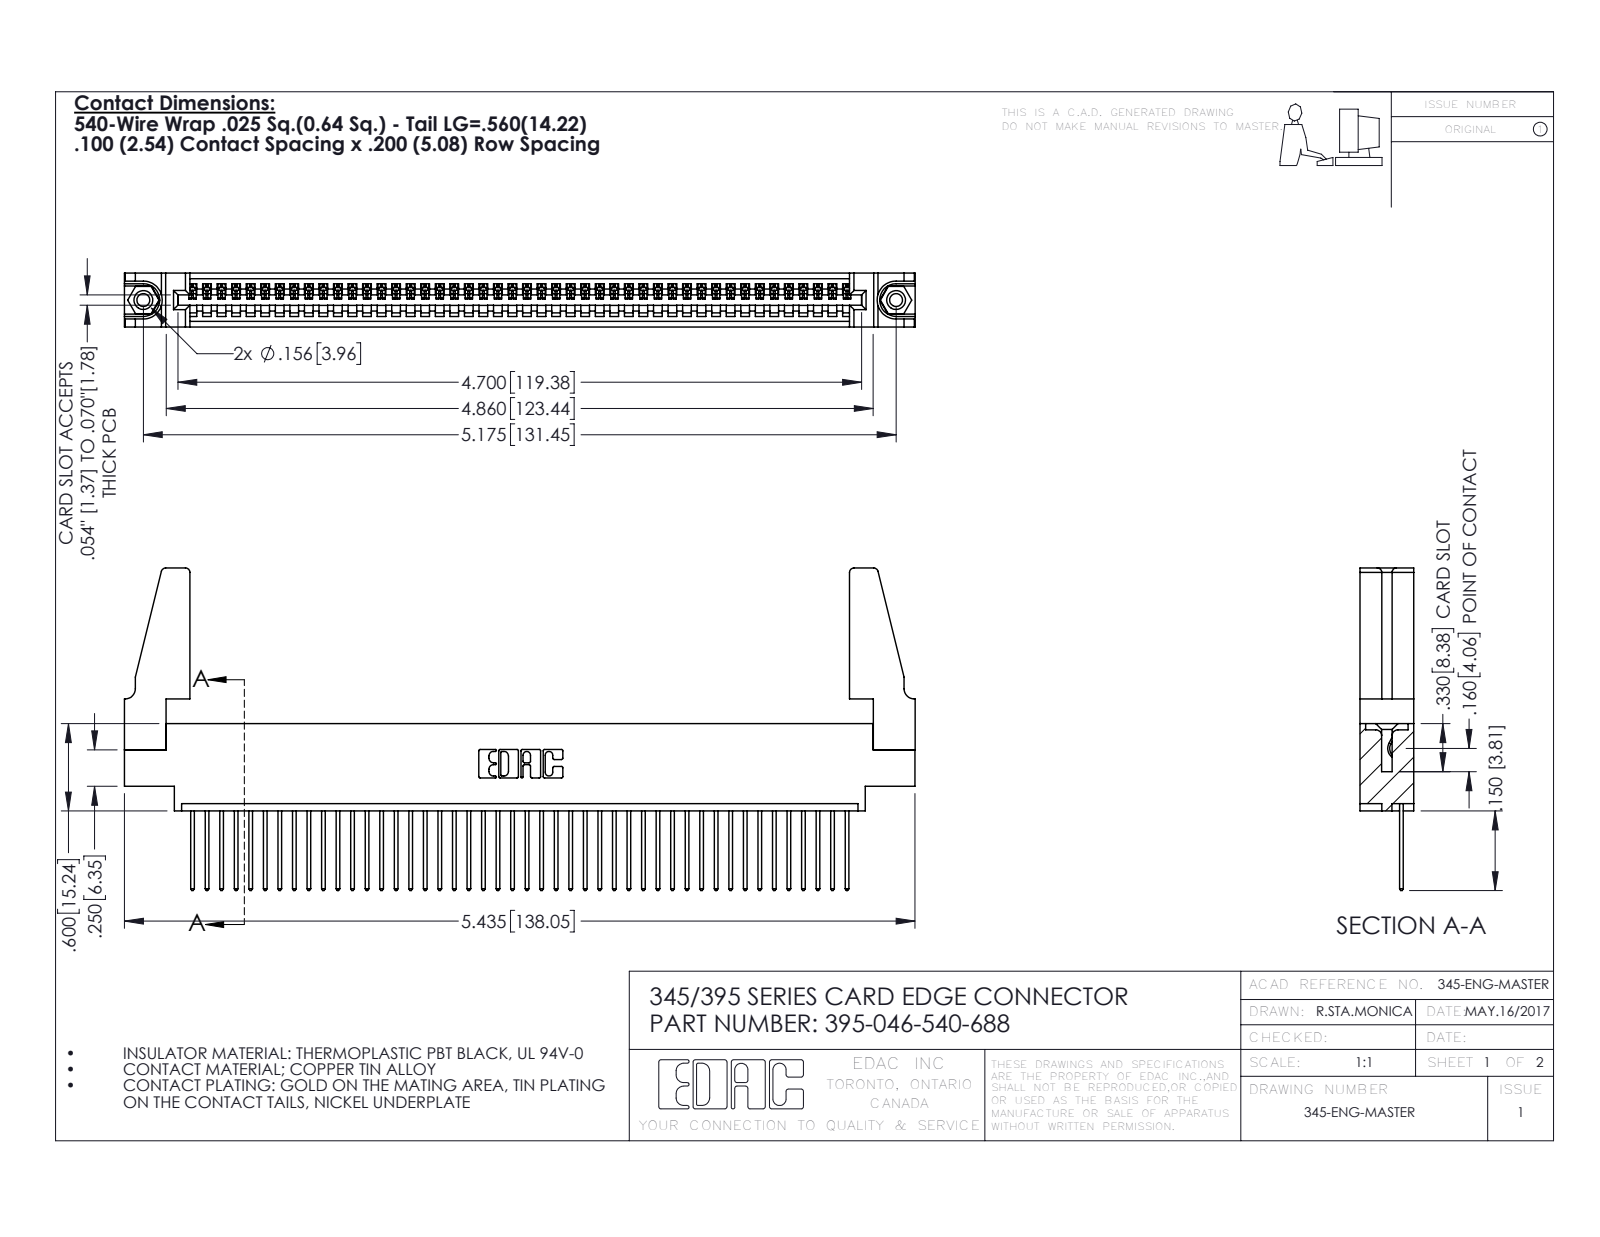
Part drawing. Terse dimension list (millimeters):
name: 345-220-078_345-220-088; 345-292-001_345-293-140; 345-250-001_345-250-001-102; 345 Part_0.170 Offset - 0.156 Dia-TH (+1 more)
written by: SolidWorks 2016 (CONFIG_CONTROL_DESIGN)
unit: mm
bodies: 51 solids, 2922 faces (1996 planar, 910 cylindrical, 16 other)
size: 138.1 × 56.3 × 9.4
volume: 16 400 mm³; area: 21 160 mm²
holes: 2× ⌀2.3, 2× ⌀3.2, 2× ⌀4, 1× ⌀1.6
bosses: 2× ⌀3.9
rounds: 92× R0.2, 92× R0.3, 22× R0.3, 8× R0.8, 6× R0.2, 6× R0.8, 3× R0.7, 2× R0.8
face distances: 1.8, 7.6, 9.4, 2.5, 6.9, 0.6, 5.1, 5.7, 4.4, 3.8
hole spacings: 6.9, 125.5, 131.4
